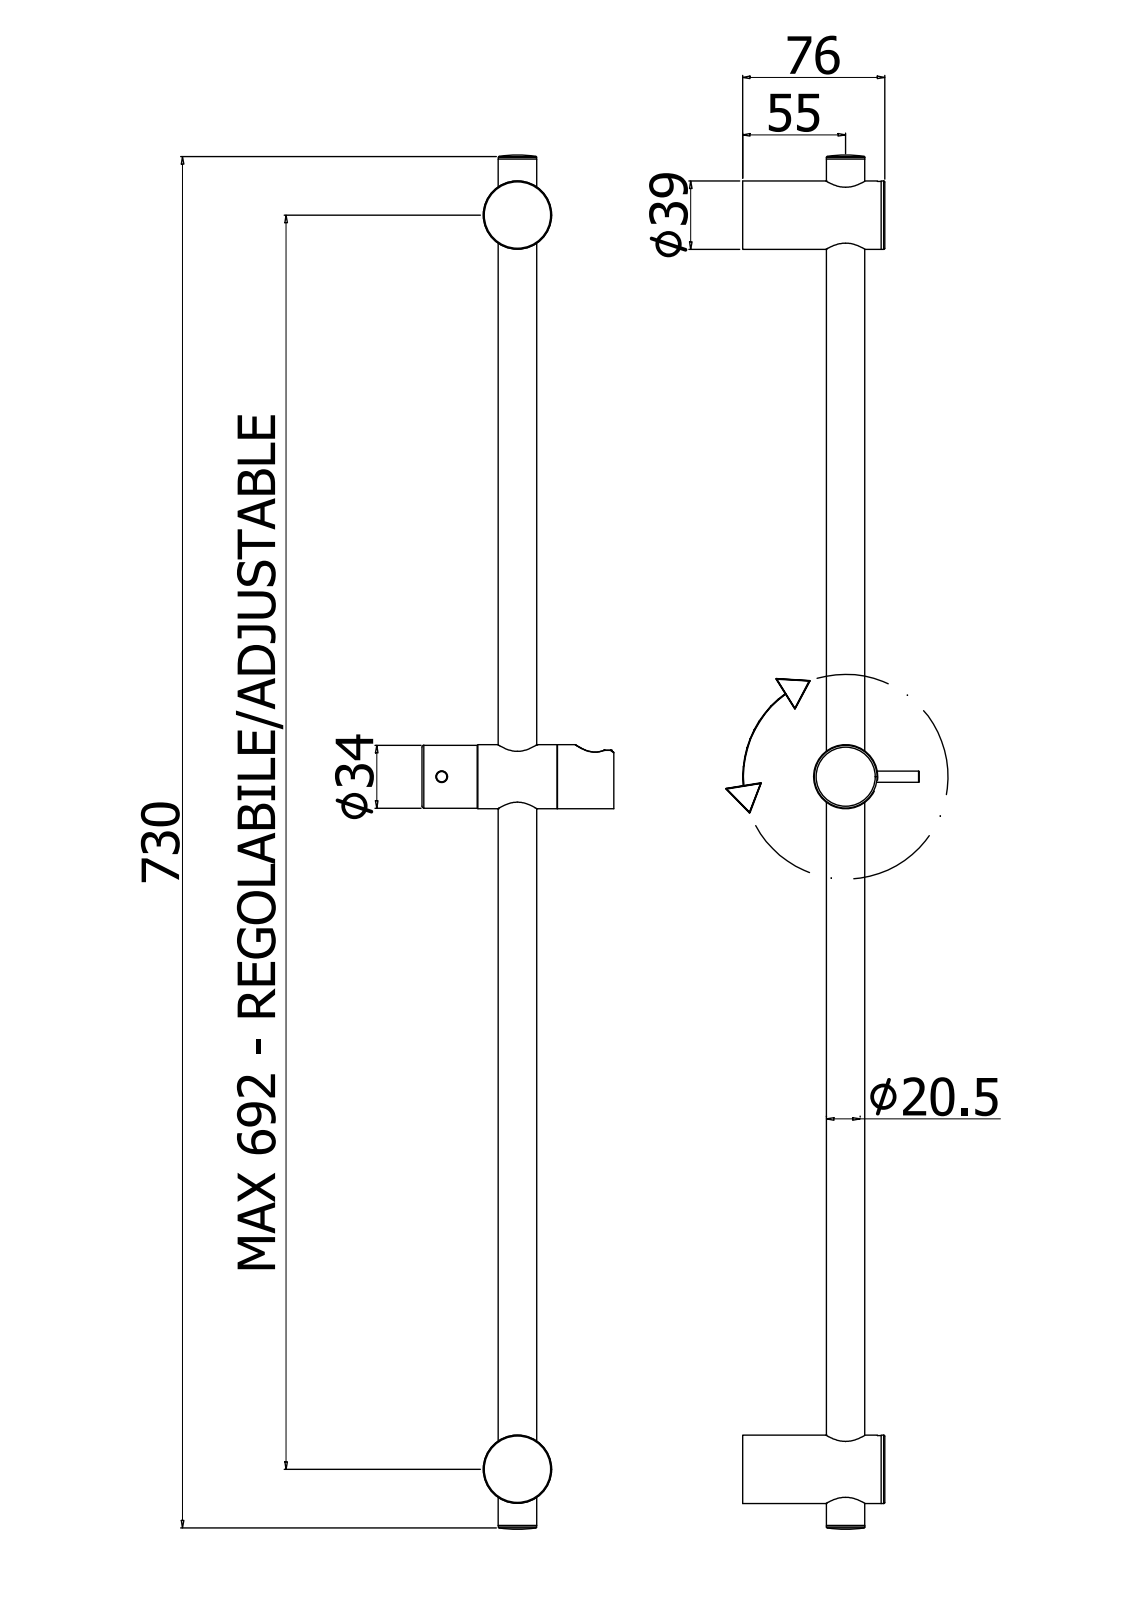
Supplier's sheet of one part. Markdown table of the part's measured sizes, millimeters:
| quantity | value |
| --- | --- |
| part name | ZSAL106CR |
| STEP written by | CREO PARAMETRIC BY PTC INC, 2020044 (CONFIG_CONTROL_DESIGN) |
| units | millimeters |
| bodies | 4 solids, 481 faces (184 planar, 170 cylindrical, 127 other) |
| overall size | 734 × 101.94 × 76.42 |
| volume | 355 463 mm³ |
| surface area | 131 770 mm² |
| round holes (diameter × count) | 31 × 3, 5.4 × 2, 11.2 × 2, 22.5 × 2, 3.8 × 1, 8 × 1, 11 × 1, 14 × 1, 18 × 1, 20 × 1, 20.8 × 1, 21 × 1 |
| round bosses / shafts (diameter × count) | 36.5 × 2, 35 × 2, 22.4 × 2, 12 × 2, 34 × 1, 32.5 × 1, 31.2 × 1, 20.6 × 1 |
| partial cylindrical surfaces (radius × count) | 1.5 × 9, 0.6 × 8, 0.5 × 6, 0.3 × 4, 12.85 × 2, 14.15 × 2, 4.1 × 1, 12.5 × 1 |
| main face-to-face distances | 1.1, 366.51, 367.61, 365.41, 2, 68.2, 70.2, 1, 74, 1.5 |
| hole center spacings | 570 |
